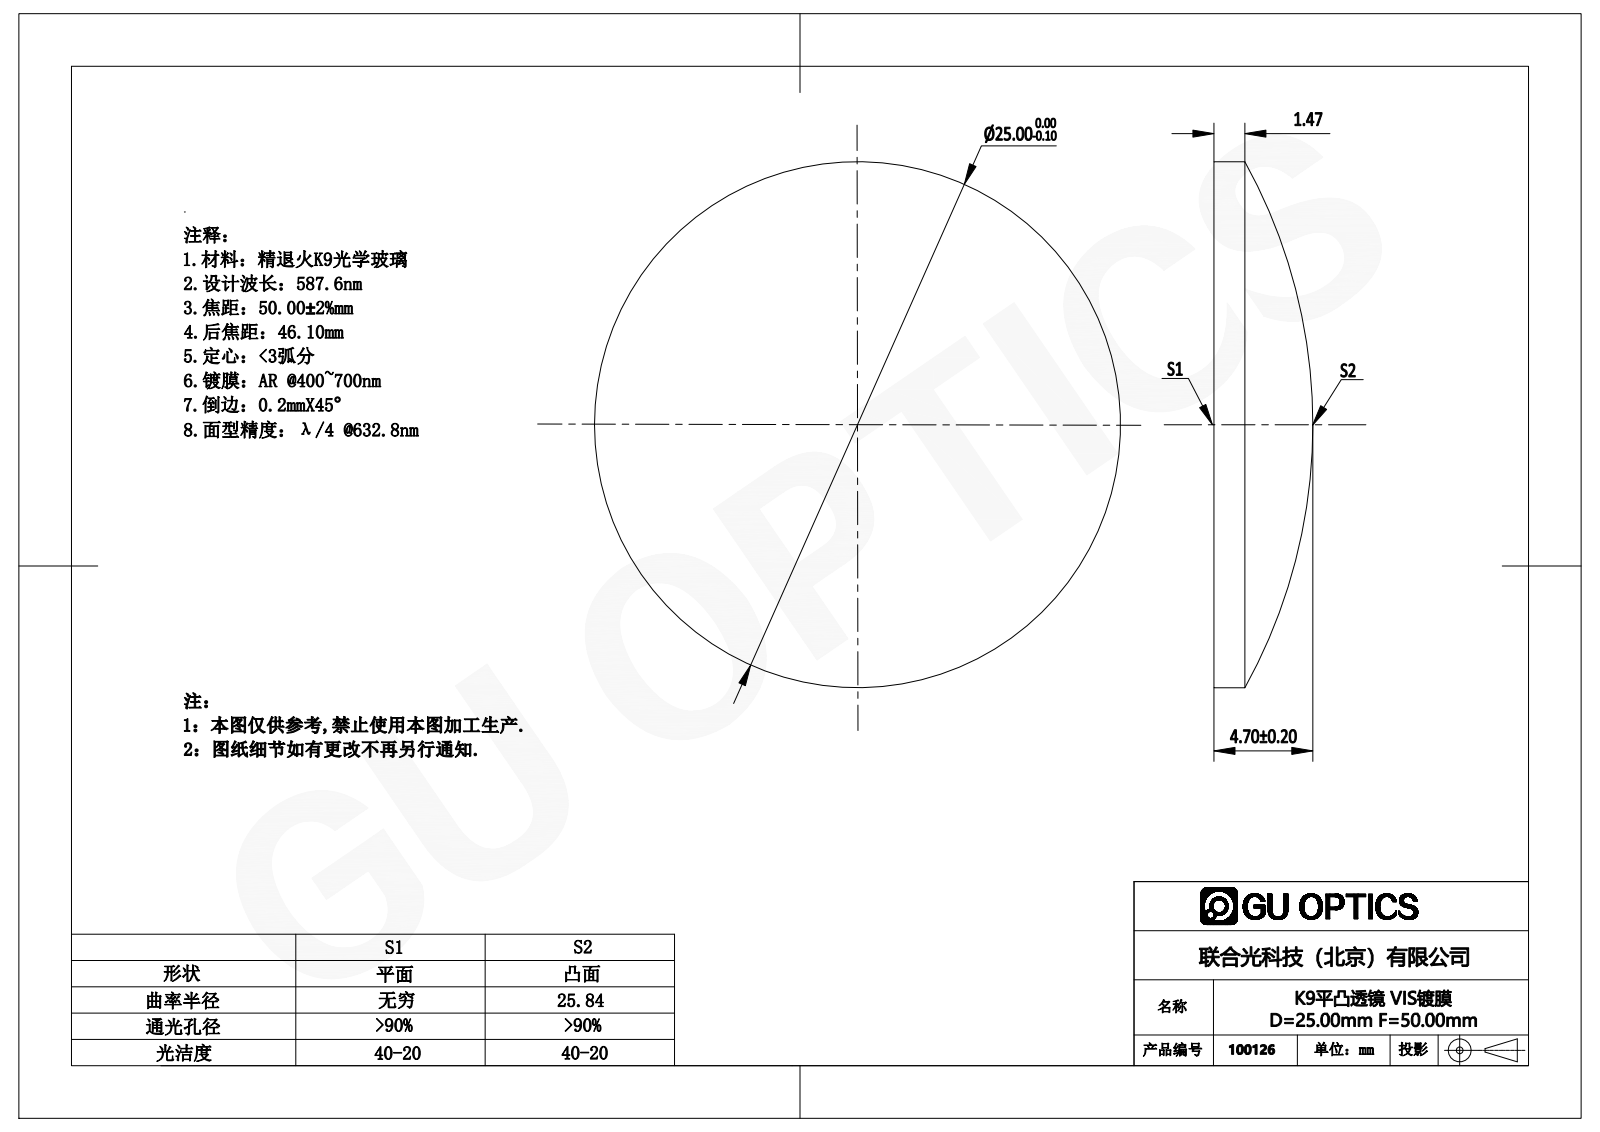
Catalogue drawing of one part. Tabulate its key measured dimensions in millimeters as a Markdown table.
| quantity | value |
| --- | --- |
| part name | 100126 |
| STEP written by | SolidWorks 2016 (AUTOMOTIVE_DESIGN) |
| units | millimeters |
| bodies | 1 solid, 5 faces (1 planar, 2 cylindrical, 2 other) |
| overall size | 25 × 25 × 4.7 |
| volume | 1 532 mm³ |
| surface area | 1 130 mm² |
| round bosses / shafts (diameter × count) | 25 × 1 |
